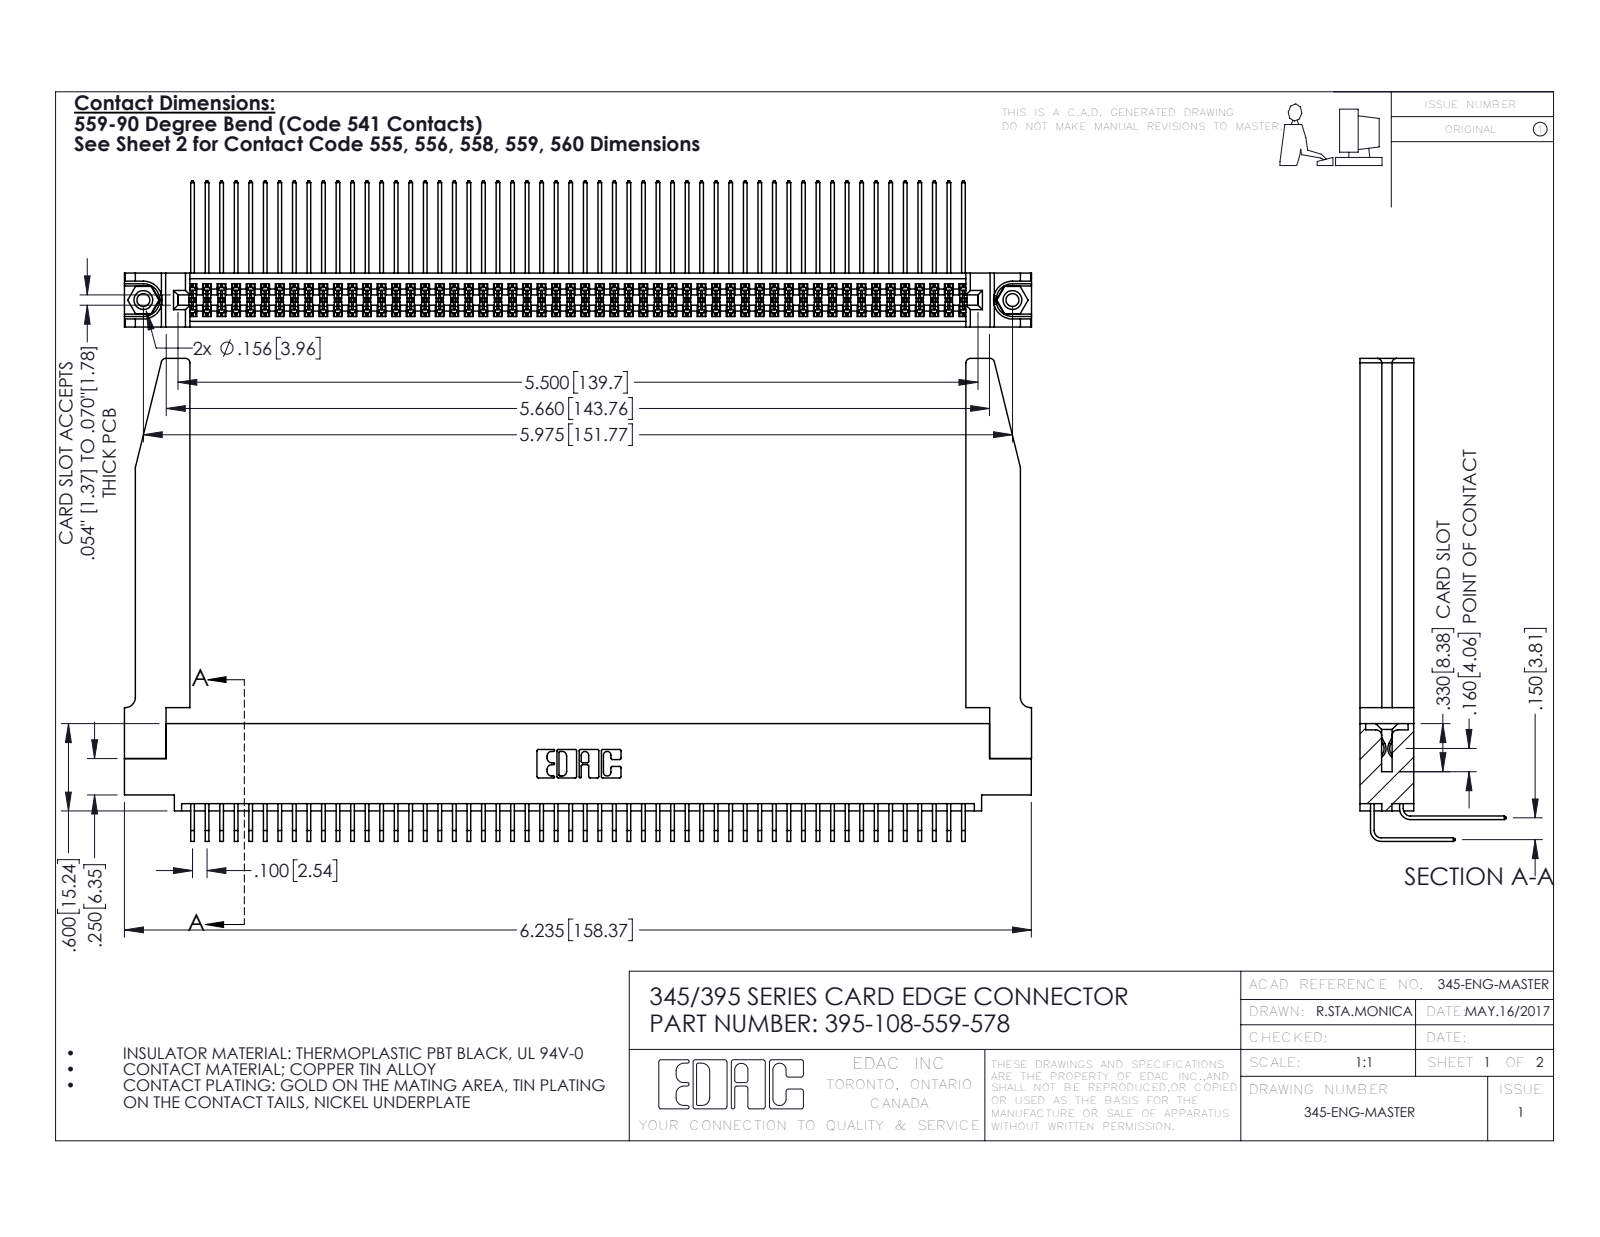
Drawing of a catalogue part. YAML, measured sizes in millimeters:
part_name: "345-250-001_345-250-001-102; 345 Part_0.110 Offset - 0.156 Dia-TH; 345-292-001_559 Tail - 2; 395-108-559-578 (+2 more)"
step_written_by: "SolidWorks 2016 (CONFIG_CONTROL_DESIGN)"
units: millimeters
bodies: {solids: 113, faces: 5980, planar: 4006, cylindrical: 1922, other: 52}
overall_size: [158.4, 84.3, 25.5]
volume: 23810
surface_area: 33810
round_holes:
  - {diameter: 2.3, count: 2}
  - {diameter: 3.2, count: 2}
  - {diameter: 4, count: 2}
  - {diameter: 1.6, count: 1}
round_bosses_or_shafts:
  - {diameter: 3.9, count: 2}
partial_cylinders:
  - {radius: 0.2, count: 162}
  - {radius: 0.3, count: 22}
  - {radius: 0.8, count: 8}
  - {radius: 0.2, count: 6}
  - {radius: 0.8, count: 6}
  - {radius: 0.7, count: 3}
  - {radius: 0.4, count: 2}
  - {radius: 0.5, count: 2}
face_to_face_distances: [1.8, 7.6, 9.4, 5.1, 2.5, 6.9, 0.6, 5.7, 4.4, 3.8]
hole_center_spacings: [6.9, 145.8, 151.8]
